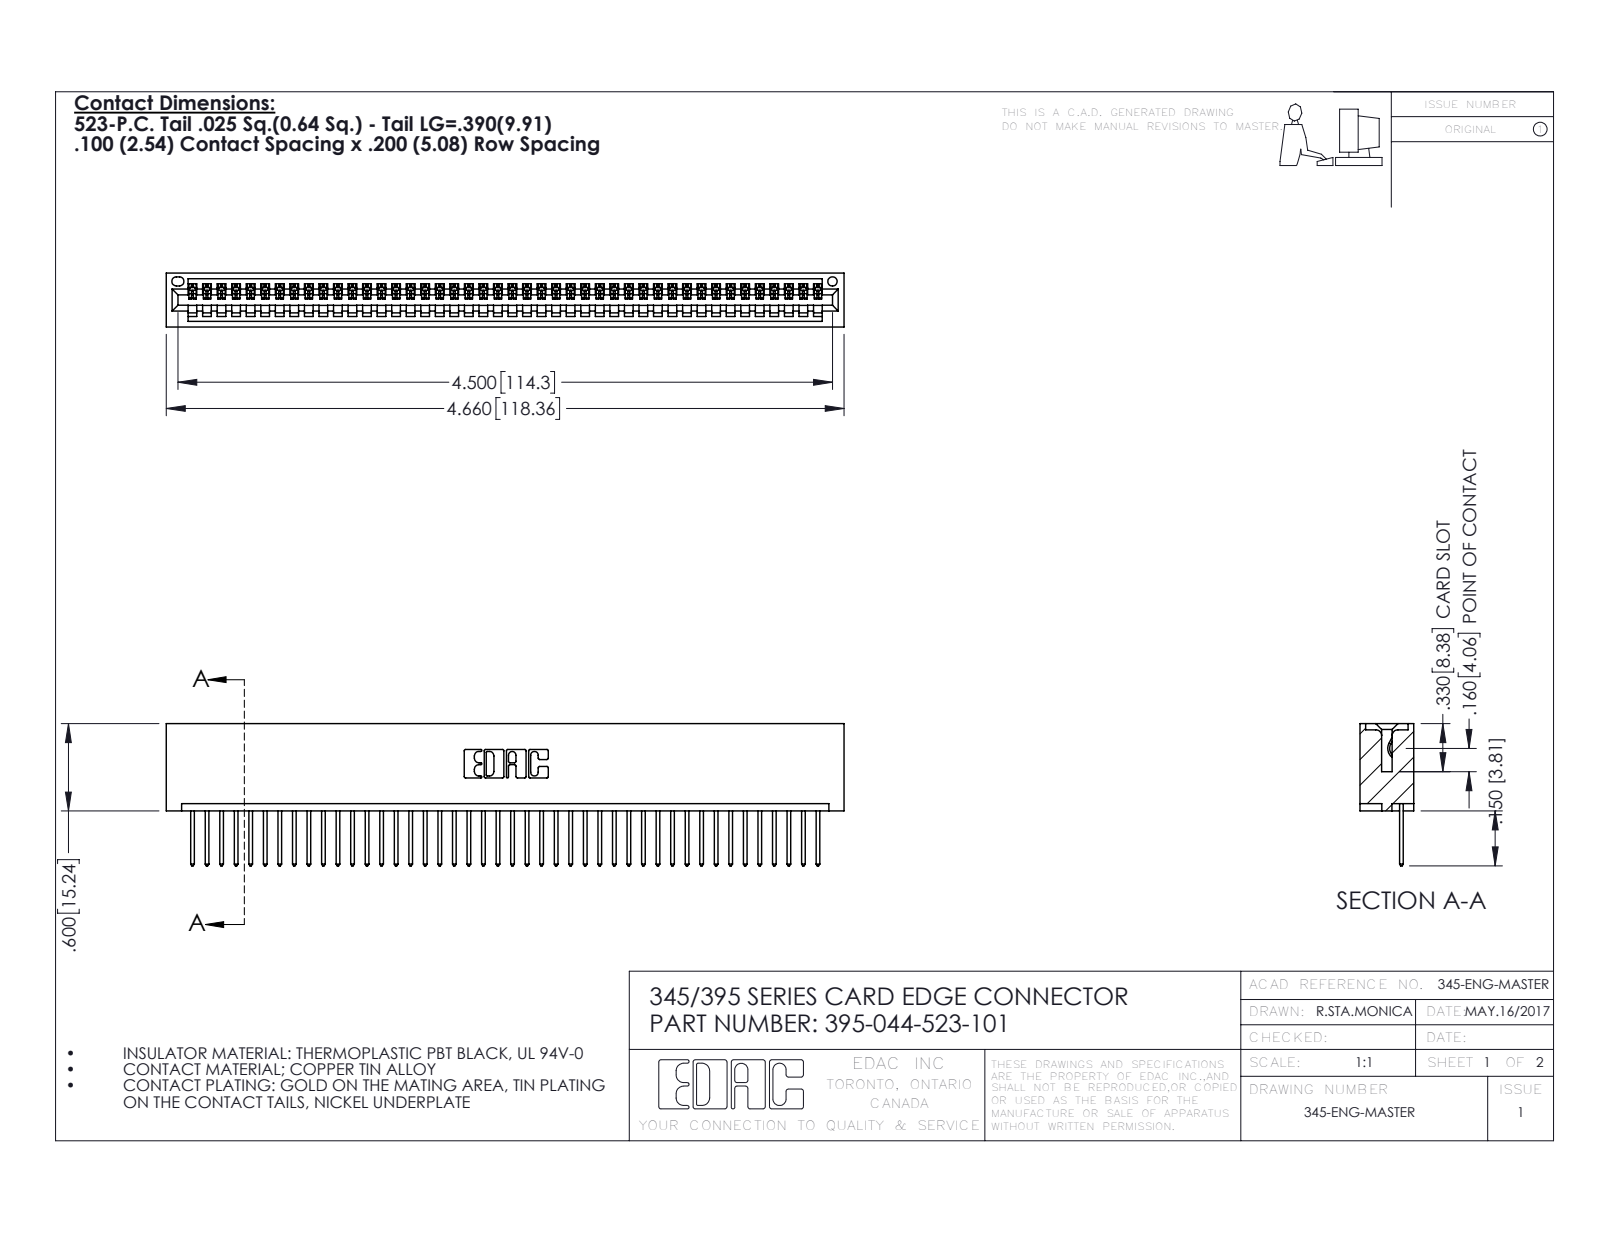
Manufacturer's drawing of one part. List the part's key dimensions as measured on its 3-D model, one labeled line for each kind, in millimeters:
Part name (STEP PRODUCT): 395-044-523-101; 345-292-001_345-293-123; 345 Part_No Mounting Lugs
STEP written by: SolidWorks 2016 (CONFIG_CONTROL_DESIGN)
Units: millimetres
Bodies: 45 solids, 2670 faces (1836 planar, 834 cylindrical, 0 other)
Overall size (bounding box): 118.4 × 24.8 × 9.4
Volume: 11 800 mm³ · Surface area: 15 980 mm²
Round holes (diameter × count): ⌀1.6 ×1
Partial cylindrical surfaces — rounded edges, fillets, slot ends (radius × count): R0.2 ×88, R0.3 ×88, R0.3 ×22, R0.2 ×6, R0.8 ×6, R0.7 ×3, R0.8 ×2, R1 ×2
Main face-to-face distances: 7.6, 1.8, 9.4, 5.1, 2.5, 6.9, 0.6, 5.7, 3.8, 1.8
